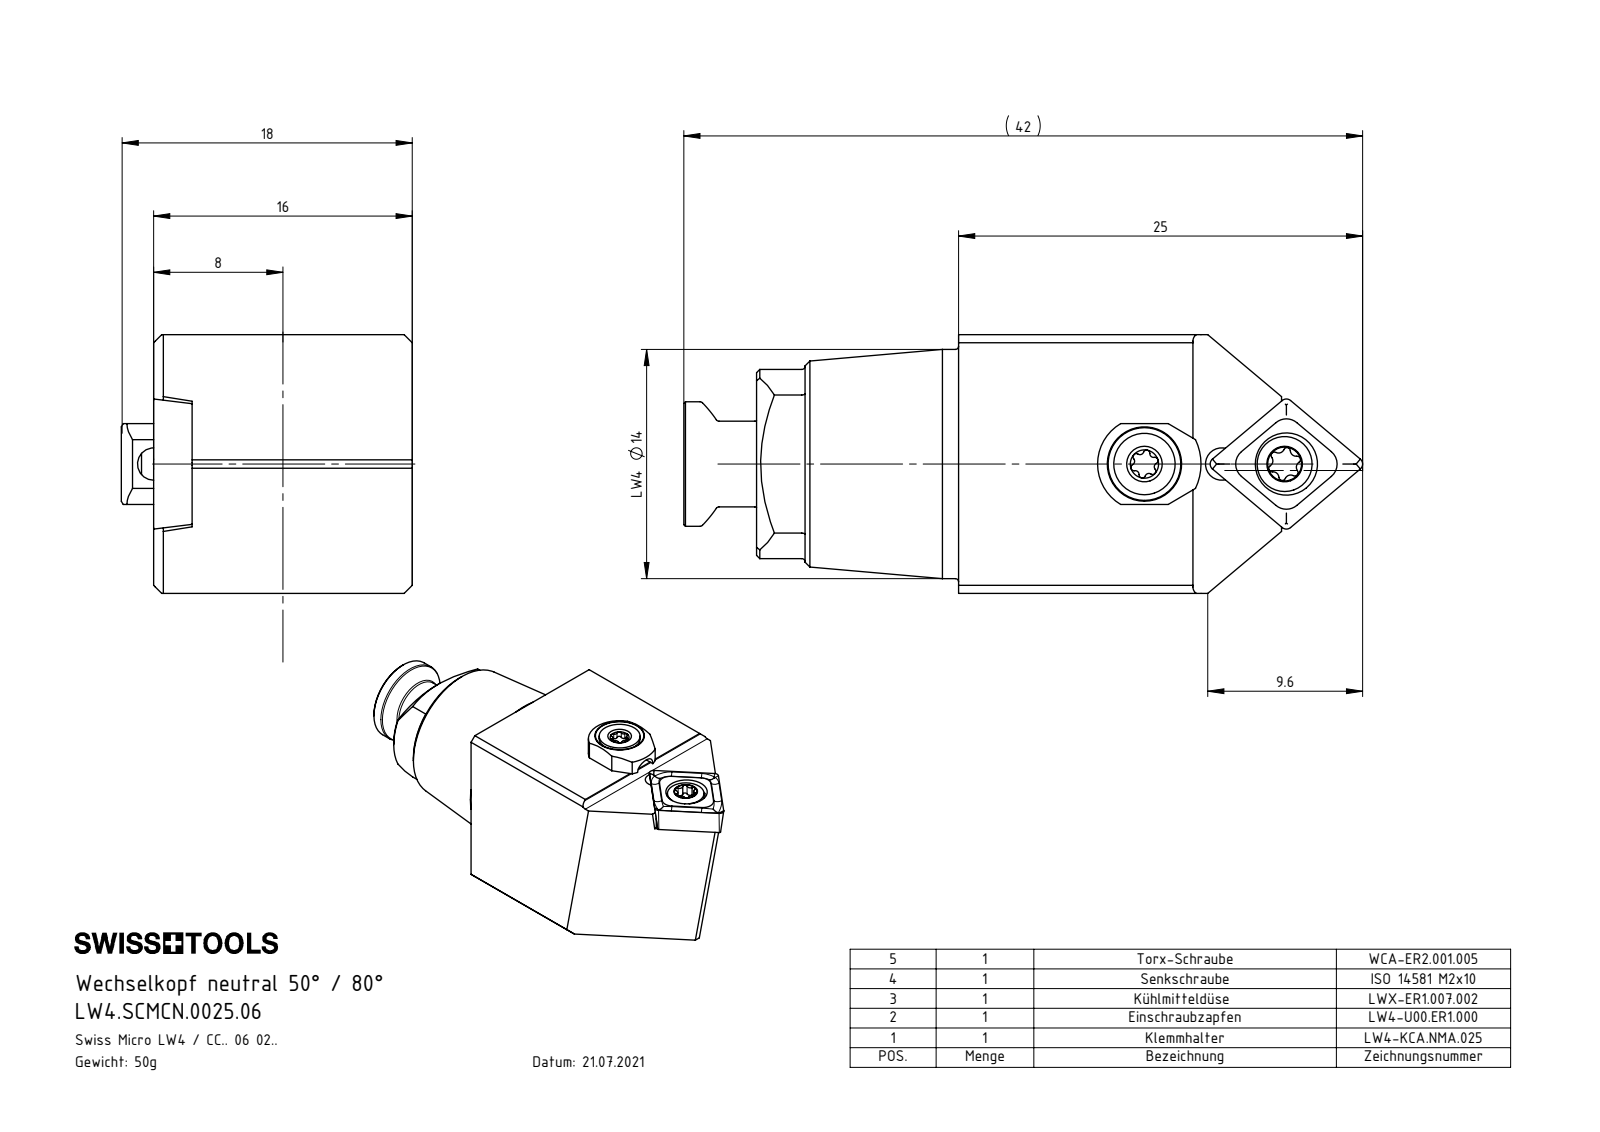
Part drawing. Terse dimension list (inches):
name: CCMT060204; LW4-KCA.NMA.025_A; ISO 14581 - M2x12; LW4.SCMCN.0025.06 (+3 more)
written by: SolidWorks 2022 (CONFIG_CONTROL_DESIGN)
unit: in
bodies: 6 solids, 255 faces (67 planar, 81 cylindrical, 107 other)
size: 1.654 × 0.768 × 0.63
volume: 0.392 in³; area: 5.369 in²
holes: 3× ⌀0.079, 2× ⌀0.118, 1× ⌀0.063, 1× ⌀0.081, 1× ⌀0.098, 1× ⌀0.11, 1× ⌀0.152, 1× ⌀0.217
bosses: 1× ⌀0.558, 1× ⌀0.303, 1× ⌀0.236, 1× ⌀0.209, 1× ⌀0.197, 1× ⌀0.15, 1× ⌀0.134, 1× ⌀0.098
rounds: 8× R0.008, 6× R0.008, 6× R0.009, 5× R0.014, 1× R0.014, 1× R0.02, 1× R0.114, 1× R0.177
face distances: 0.63, 0.295, 0.536, 0.094, 0.413, 0.492, 0.606, 0.07, 0.024, 0.079
hole spacings: 0.153, 0.157, 0.188, 0.341, 0.346
